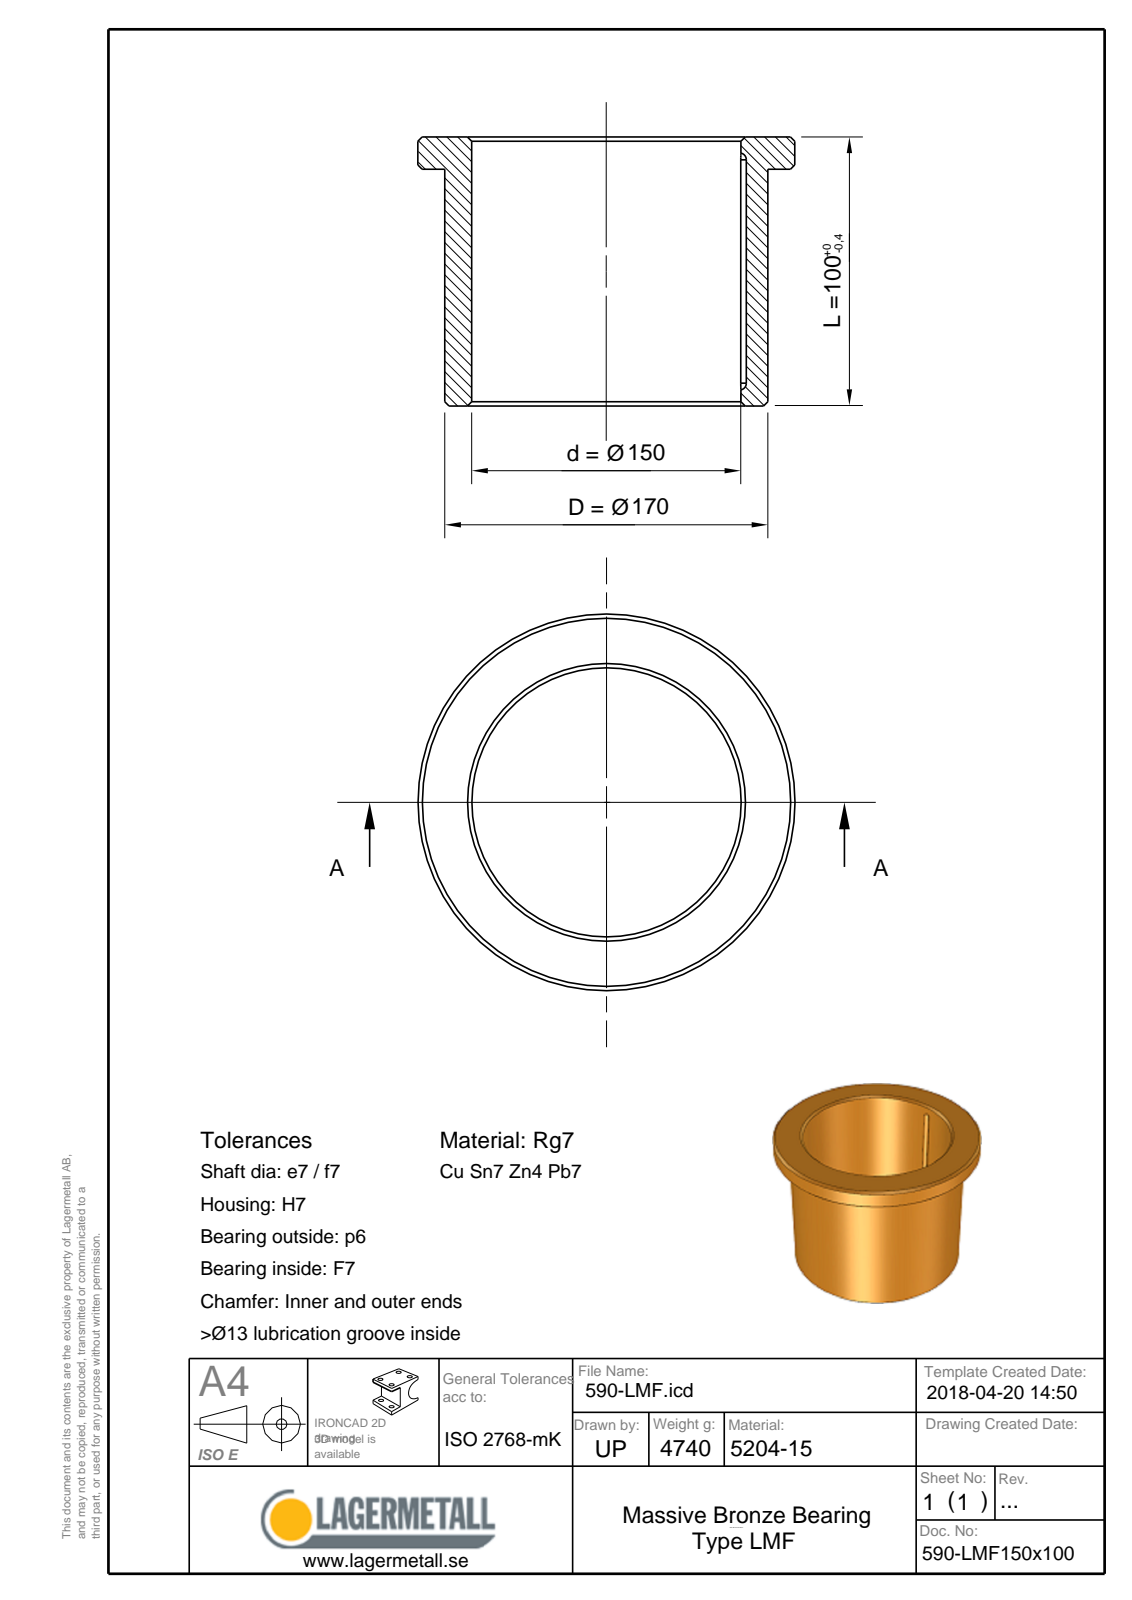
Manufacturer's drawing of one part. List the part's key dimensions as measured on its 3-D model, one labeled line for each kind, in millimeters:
Part name (STEP PRODUCT): 590-LMF150x100
STEP written by: Spatial InterOp 3D (CONFIG_CONTROL_DESIGN)
Units: millimetres
Bodies: 1 solid, 16 faces (4 planar, 5 cylindrical, 7 other)
Overall size (bounding box): 185 × 185 × 100
Volume: 538 596 mm³ · Surface area: 116 520 mm²
Round holes (diameter × count): ⌀150 ×1
Round bosses / shafts (diameter × count): ⌀185 ×1, ⌀170 ×1
Partial cylindrical surfaces — rounded edges, fillets, slot ends (radius × count): R2.25 ×2
Main face-to-face distances: 10, 90, 100
